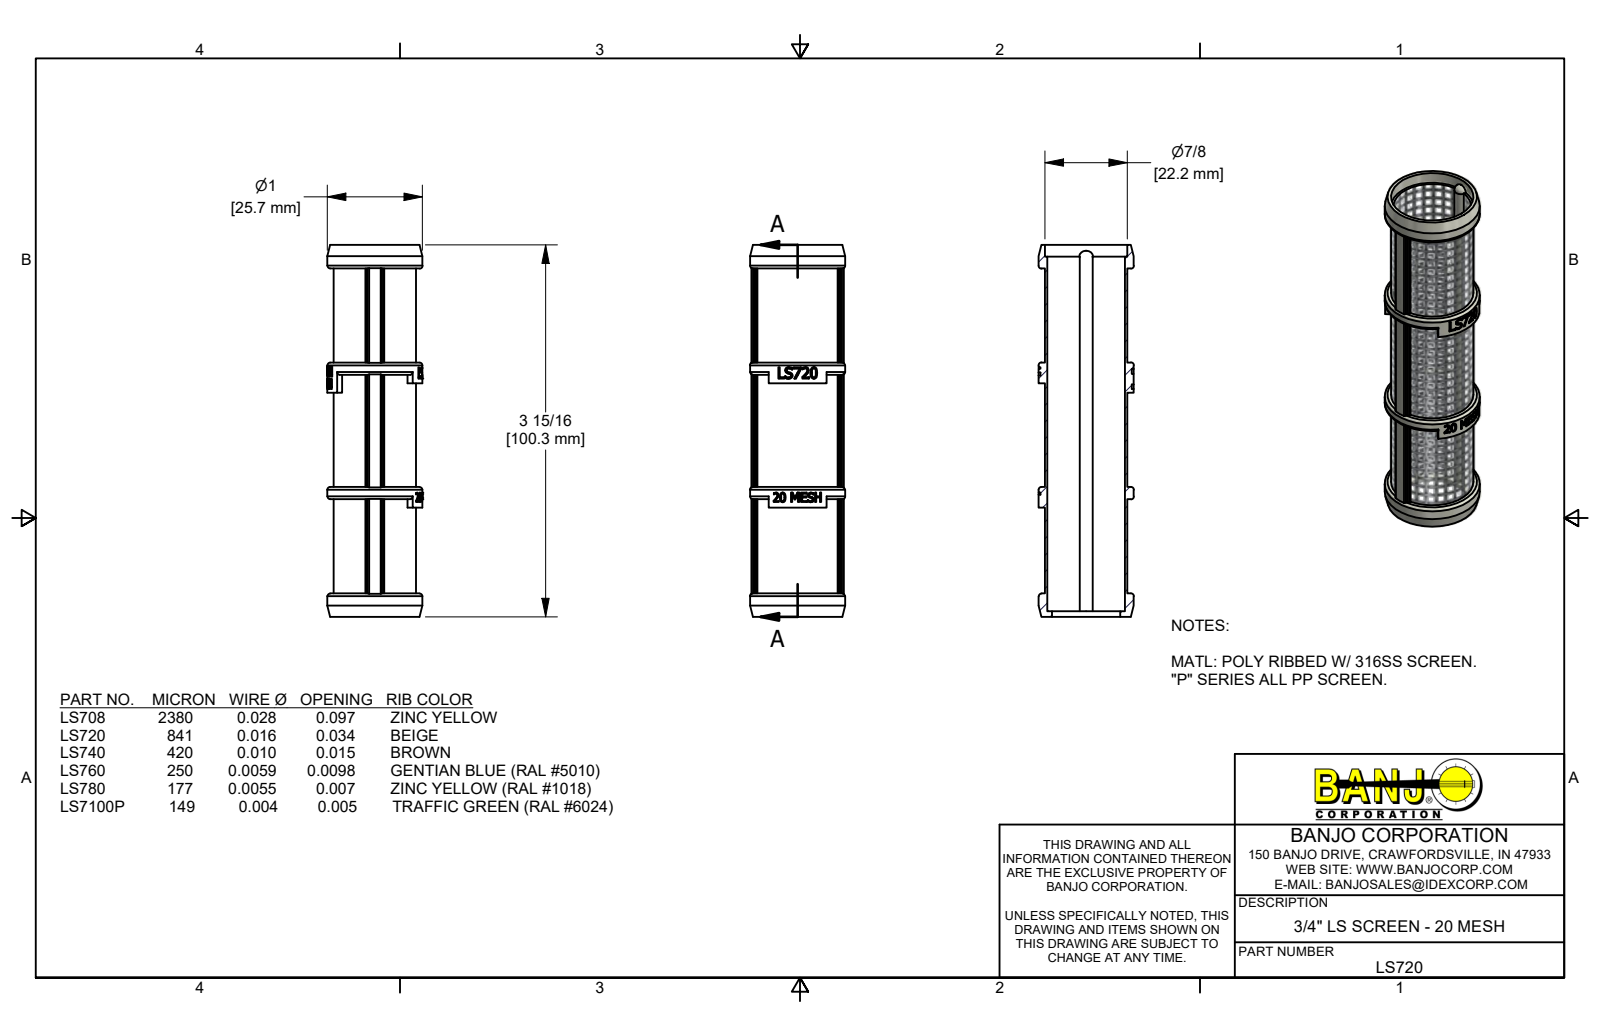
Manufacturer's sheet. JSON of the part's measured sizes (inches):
{"part_name": "LS720", "step_written_by": "Autodesk Inventor 2019 (AUTOMOTIVE_DESIGN)", "units": "inches", "bodies": {"solids": 1, "faces": 440, "planar": 215, "cylindrical": 88, "other": 137}, "overall_size": [3.95, 1.01, 1.01], "volume_in3": 0.509, "surface_area_in2": 24.04, "round_holes": [[0.725, 1], [0.825, 1]], "round_bosses_or_shafts": [[1.01, 1], [0.875, 1]], "partial_cylinders_radius": [[0.015, 8], [0.075, 2], [0.46, 1], [0.485, 1], [0.49, 1]], "face_to_face_distances": [0.25, 3.7, 1.322, 2.321, 1.249, 2.701, 0.999, 2.451, 1.379, 2.571]}
